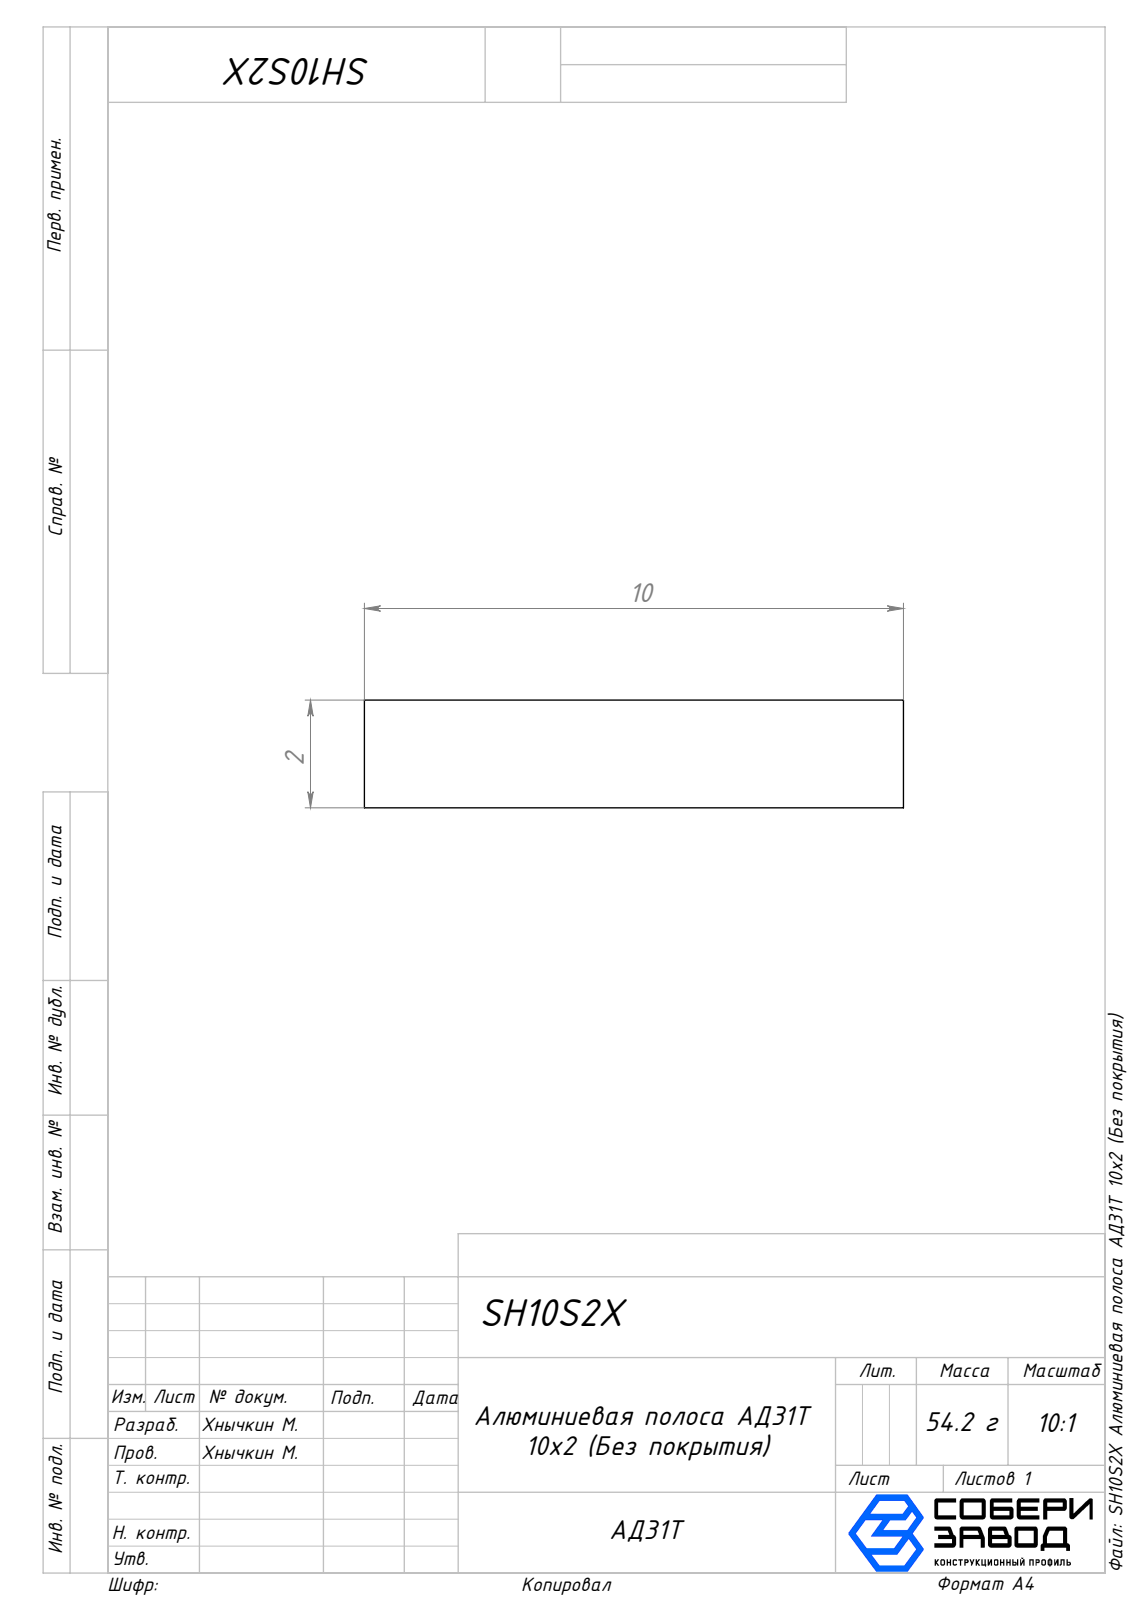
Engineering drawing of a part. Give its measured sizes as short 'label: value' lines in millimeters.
name: SH10S2X Алюминиевая полоса АД31Т 10х2 (Без покрытия)
written by: SolidWorks 2025 (AUTOMOTIVE_DESIGN)
unit: mm
bodies: 1 solid, 6 faces (6 planar, 0 cylindrical, 0 other)
size: 1000 × 10 × 2
volume: 20 000 mm³; area: 24 040 mm²
face distances: 2, 10, 1000
